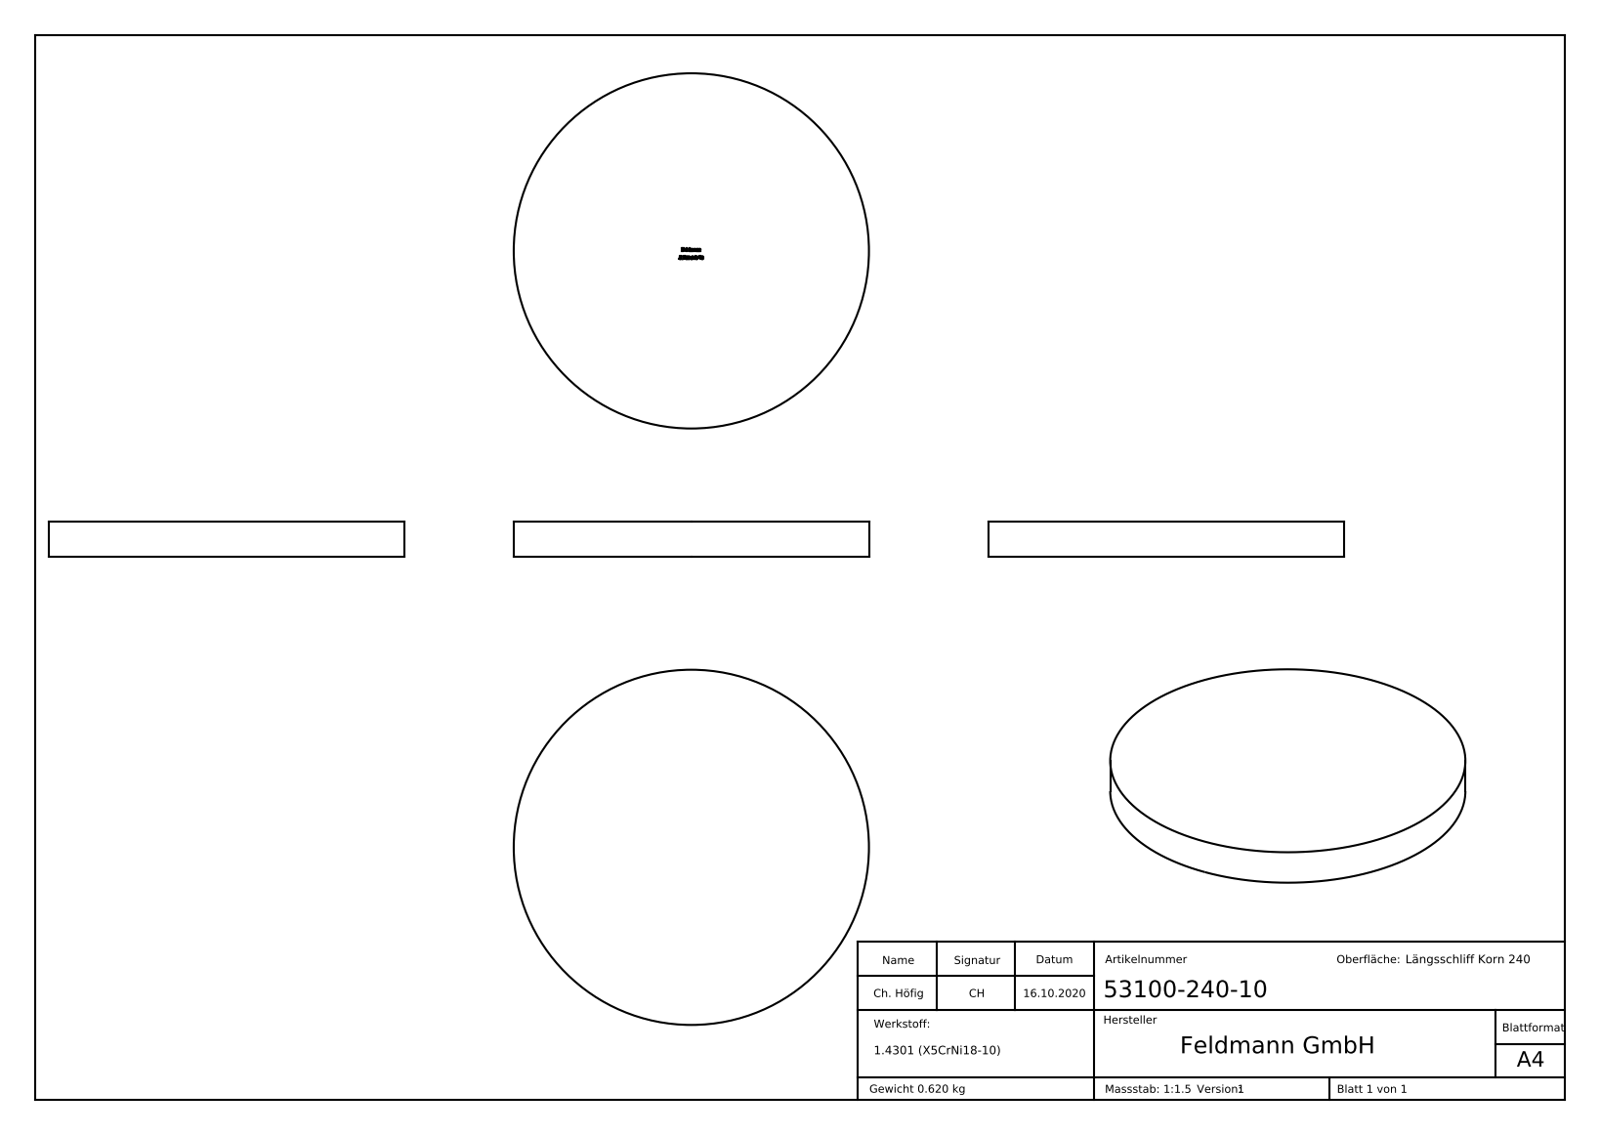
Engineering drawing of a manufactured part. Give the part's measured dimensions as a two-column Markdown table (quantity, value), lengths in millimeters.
| quantity | value |
| --- | --- |
| part name | 53100-240-10 |
| STEP written by | SolidWorks 2018 (CONFIG_CONTROL_DESIGN) |
| units | millimeters |
| bodies | 1 solid, 246 faces (132 planar, 2 cylindrical, 112 other) |
| overall size | 100 × 100 × 10 |
| volume | 78 540 mm³ |
| surface area | 18 856 mm² |
| round bosses / shafts (diameter × count) | 100 × 1 |
| main face-to-face distances | 10, 9.9, 1.06, 2.45, 0.99, 0.39, 2.77, 1.55, 1.78, 0.83 |
